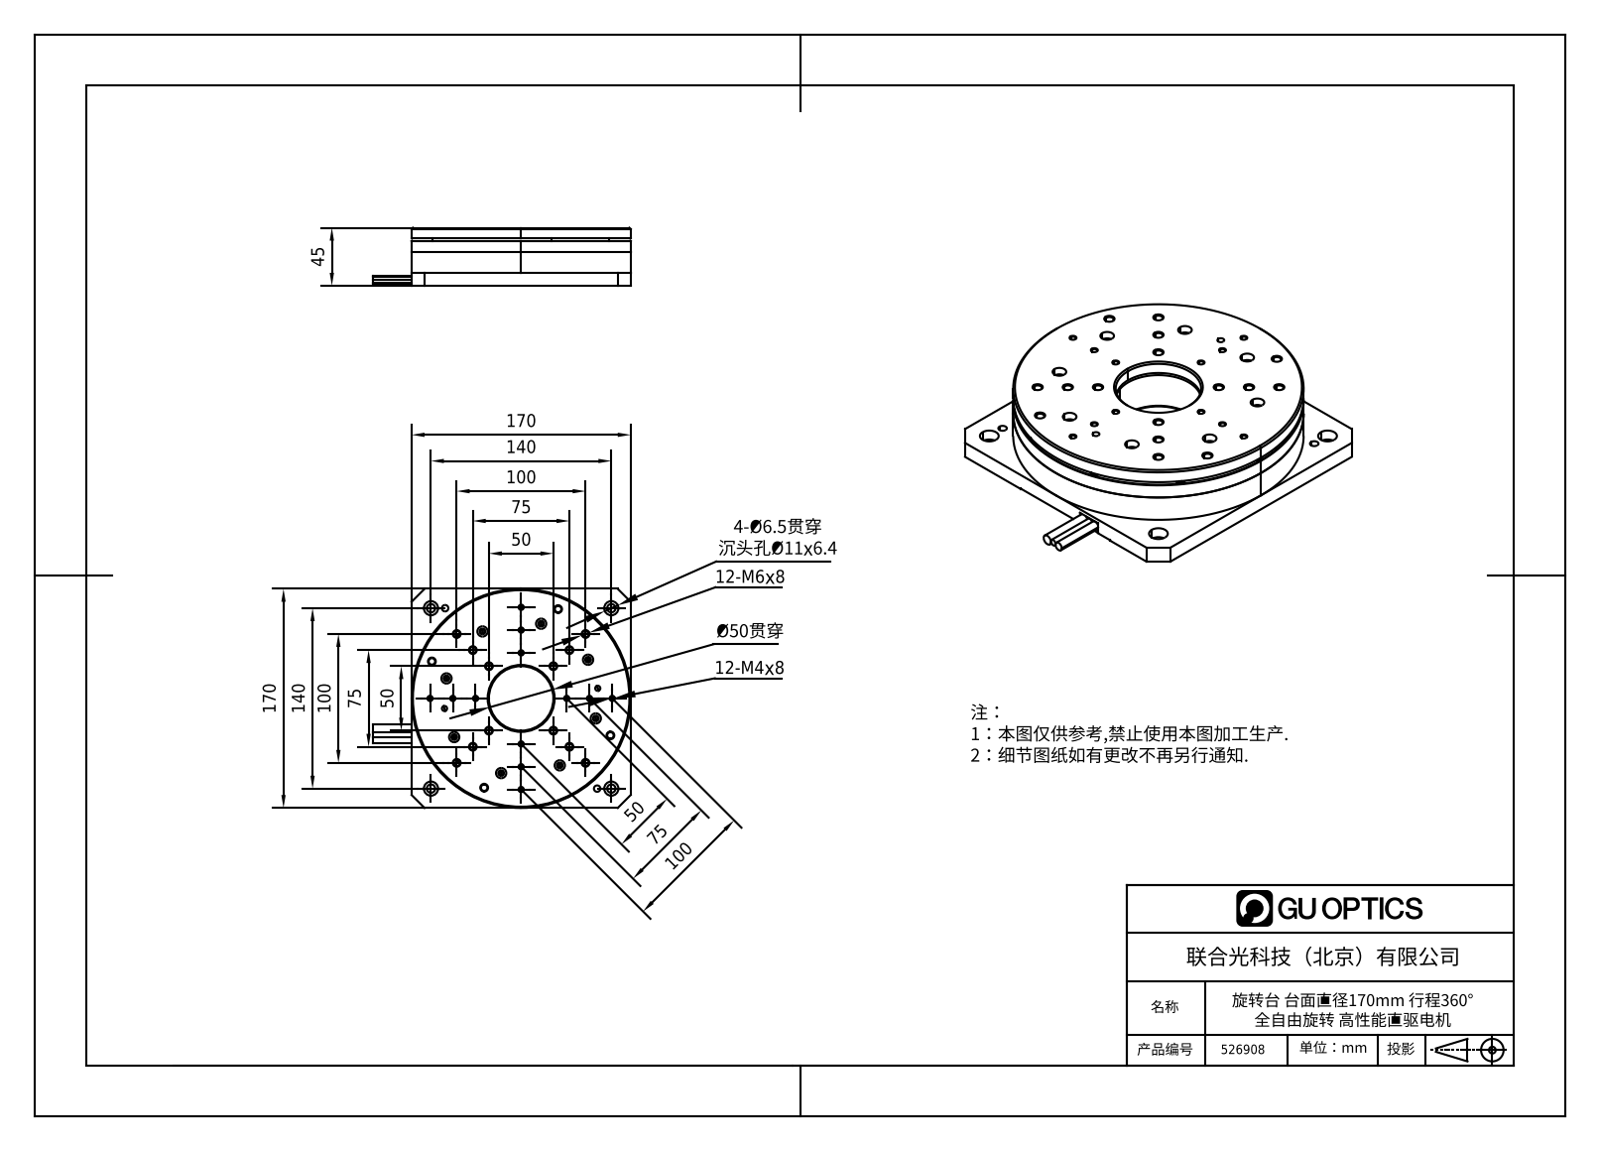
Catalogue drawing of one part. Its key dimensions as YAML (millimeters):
part_name: "FMSR170D"
step_written_by: "SolidWorks 2017 (AUTOMOTIVE_DESIGN)"
units: millimeters
bodies: {solids: 4, faces: 526, planar: 207, cylindrical: 235, other: 84}
overall_size: [200, 170, 45]
volume: 943779
surface_area: 195236
round_holes:
  - {diameter: 5, count: 18}
  - {diameter: 3.3, count: 12}
  - {diameter: 6, count: 10}
  - {diameter: 3.2, count: 8}
  - {diameter: 4.5, count: 8}
  - {diameter: 7.5, count: 8}
  - {diameter: 8, count: 8}
  - {diameter: 6.5, count: 4}
  - {diameter: 11, count: 4}
  - {diameter: 4, count: 2}
  - {diameter: 50, count: 1}
  - {diameter: 95, count: 1}
round_bosses_or_shafts:
  - {diameter: 5.5, count: 10}
  - {diameter: 6.8, count: 8}
  - {diameter: 170, count: 1}
  - {diameter: 137, count: 1}
  - {diameter: 6, count: 1}
  - {diameter: 5.2, count: 1}
  - {diameter: 3.8, count: 1}
face_to_face_distances: [8, 23.5, 0.5, 36.7, 44.7, 11, 19, 25.7, 10, 35]
hole_center_spacings: [60, 36.56, 45.92, 56.12, 61.5, 93.08, 107.77, 110.87]
